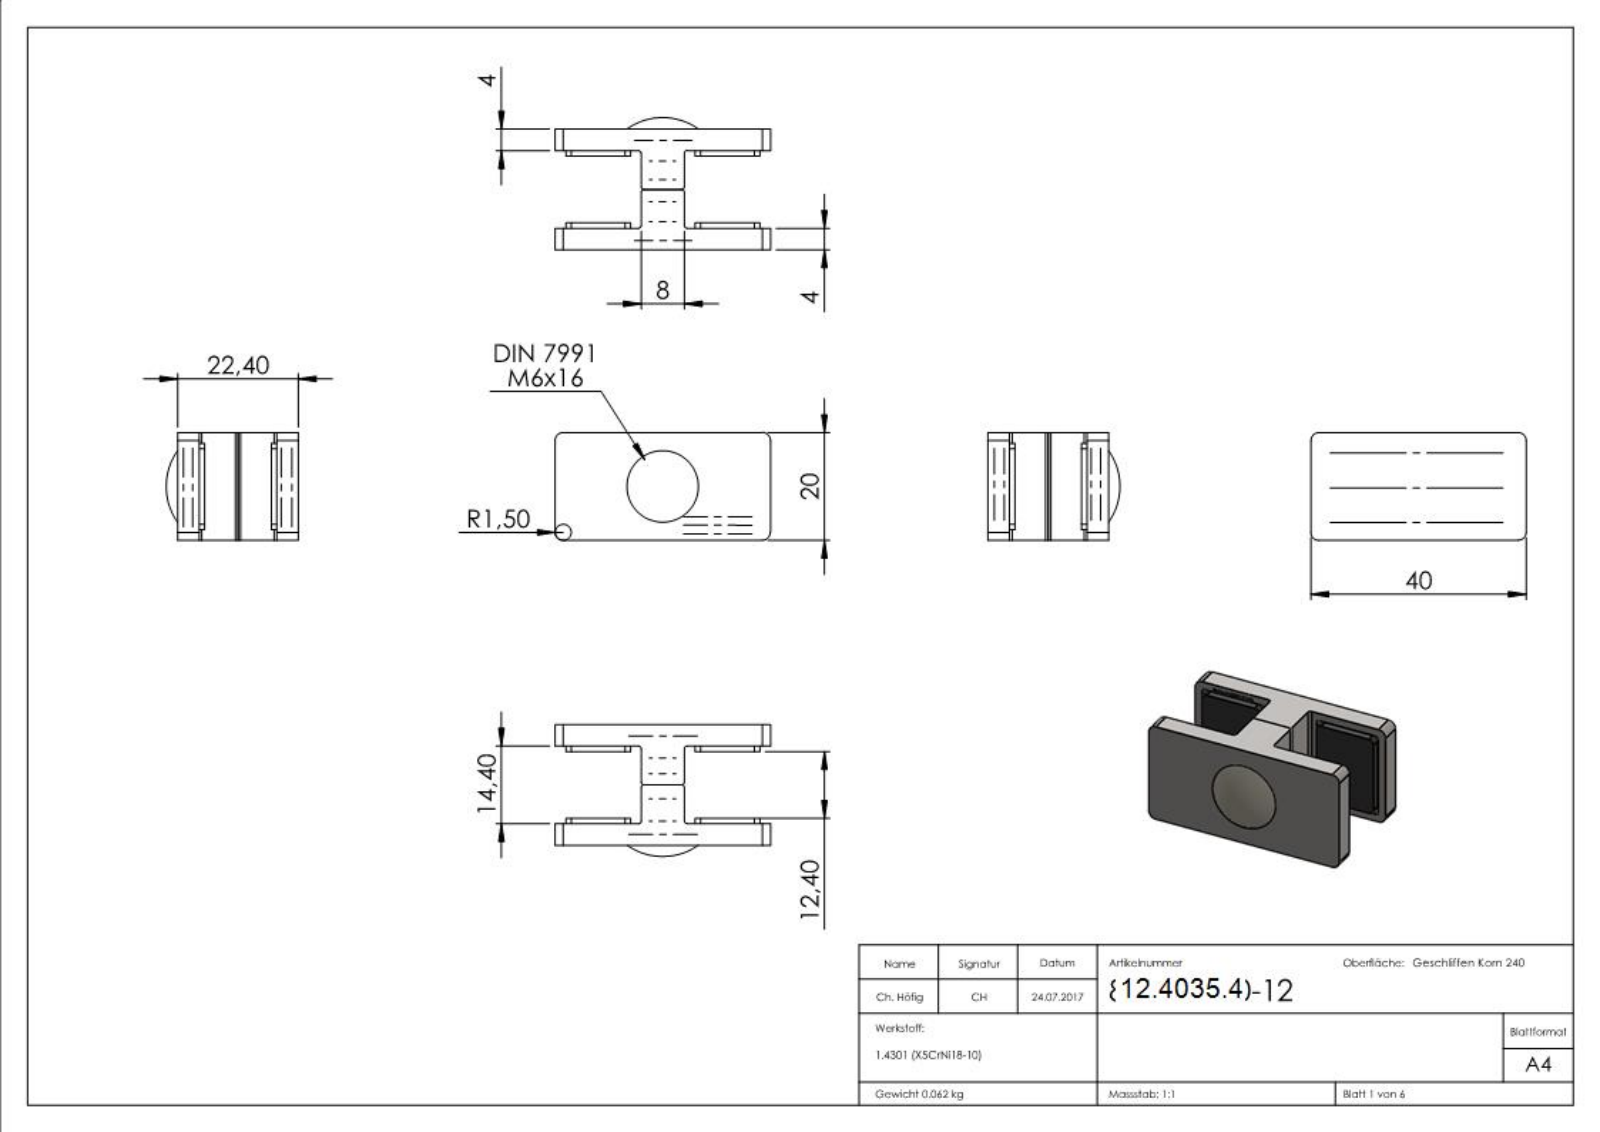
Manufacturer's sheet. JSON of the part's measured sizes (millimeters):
{"part_name": "80570-XXX-XX Teil1_80570-240-12 Teil1; DIN7991 M6xXX; DIN7991 M6xXX_DIN7991 M6x16; 80570-240-12 (+7 more)", "step_written_by": "SolidWorks 2018 (CONFIG_CONTROL_DESIGN)", "units": "millimeters", "bodies": {"solids": 8, "faces": 825, "planar": 383, "cylindrical": 203, "other": 239}, "overall_size": [40, 28.06, 20], "volume_mm3": 9134, "surface_area_mm2": 8473, "round_holes": [[2.7, 2], [1.8, 1], [5, 1], [6.5, 1], [12.5, 1]], "round_bosses_or_shafts": [[12, 1], [6, 1], [4, 1]], "partial_cylinders_radius": [[0.5, 80], [0.2, 12], [1, 8], [0.19, 4], [1.5, 4]], "face_to_face_distances": [3.5, 18.9, 1.5, 5, 22.4, 17.4, 13.9, 15.4, 2, 0.5], "hole_center_spacings": [6.5, 13]}
